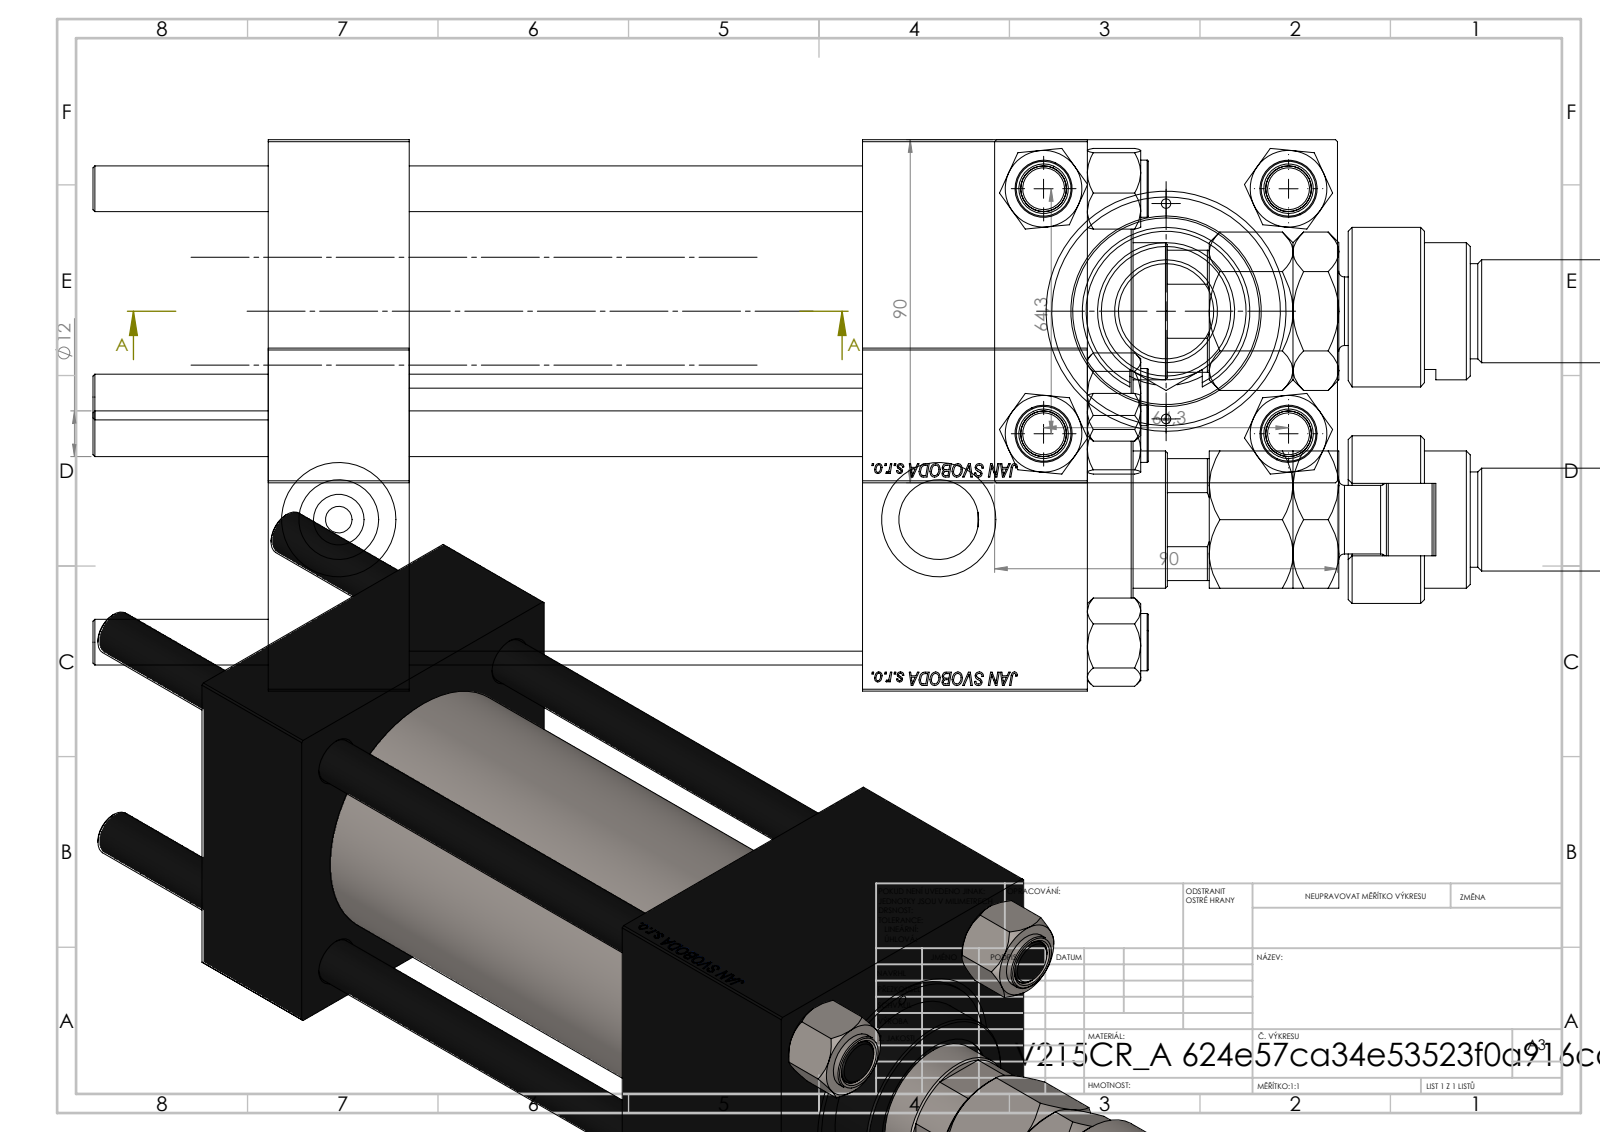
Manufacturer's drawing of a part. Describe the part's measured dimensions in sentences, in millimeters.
The part is named "MFA; V215CR_BODY_A; FEMALE_PART_FOR_DFA; NUT_M5 (+3 more)". Its 3-D file was written by "SolidWorks 2019 (CONFIG_CONTROL_DESIGN)". It is 13 solids with 1225 faces: 550 planar, 95 cylindrical and 580 other. Overall it measures 403.5 by 90 by 90 millimeters. Its volume is 1 227 000 cubic millimeters and its surface area 262 281 square millimeters. Round holes: 4 of diameter 12, 2 of diameter 2.5, 2 of diameter 7, 2 of diameter 20.96, 2 of diameter 30, 1 of diameter 25.5, 1 of diameter 39, 1 of diameter 50, 1 of diameter 60, 1 of diameter 63. Round bosses or shafts: 4 of diameter 15, 1 of diameter 69, 1 of diameter 44, 1 of diameter 36, 1 of diameter 28, 1 of diameter 27, 1 of diameter 25, 1 of diameter 18. Partial cylindrical surfaces (rounded edges, fillets, slot ends): 1 of radius 9.5, 1 of radius 15, 1 of radius 17.5. The main face-to-face distances are 90, 37, 215, 178, 59, 156, 119, 186.3, 149.3, 30.3. The hole center spacings are 32.39, 45.47, 64.3, 68.42, 28.25, 90.93, 56.5, 157.5.
